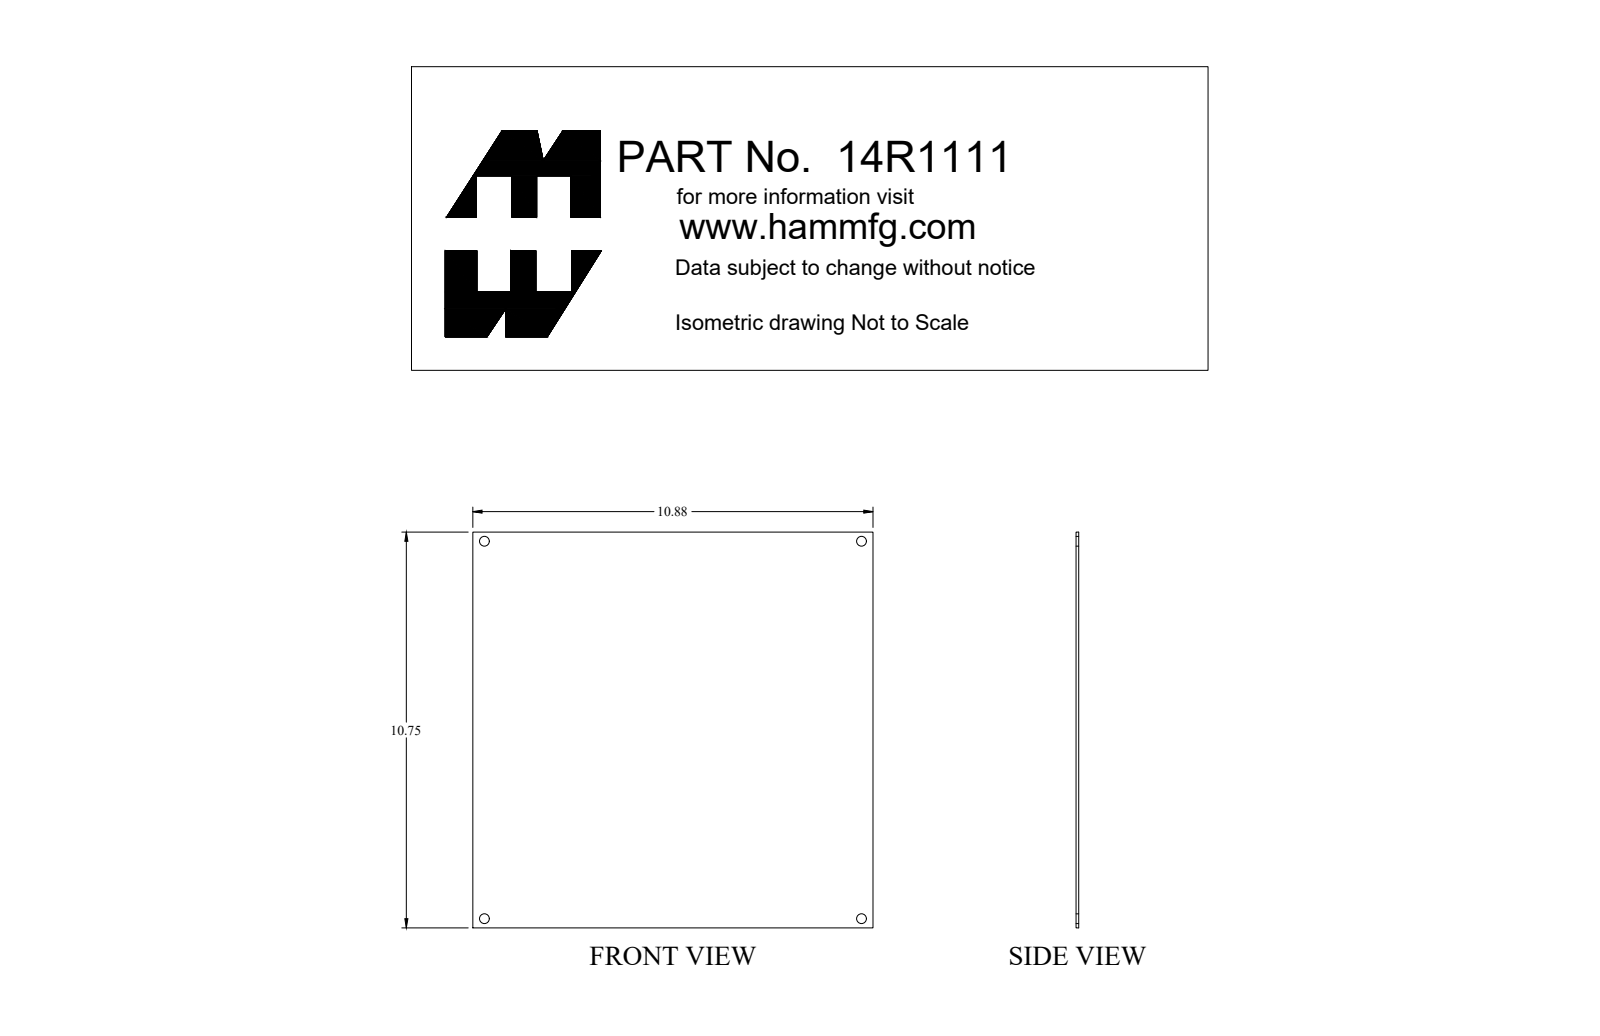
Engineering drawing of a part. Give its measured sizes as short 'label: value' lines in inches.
name: 14R1111
written by: SolidWorks 2018 (AUTOMOTIVE_DESIGN)
unit: in
bodies: 1 solid, 10 faces (6 planar, 4 cylindrical, 0 other)
size: 10.875 × 10.75 × 0.072
volume: 8.401 in³; area: 236.7 in²
holes: 4× ⌀0.265
face distances: 0.072, 10.75, 10.875
hole spacings: 10.25, 14.496
